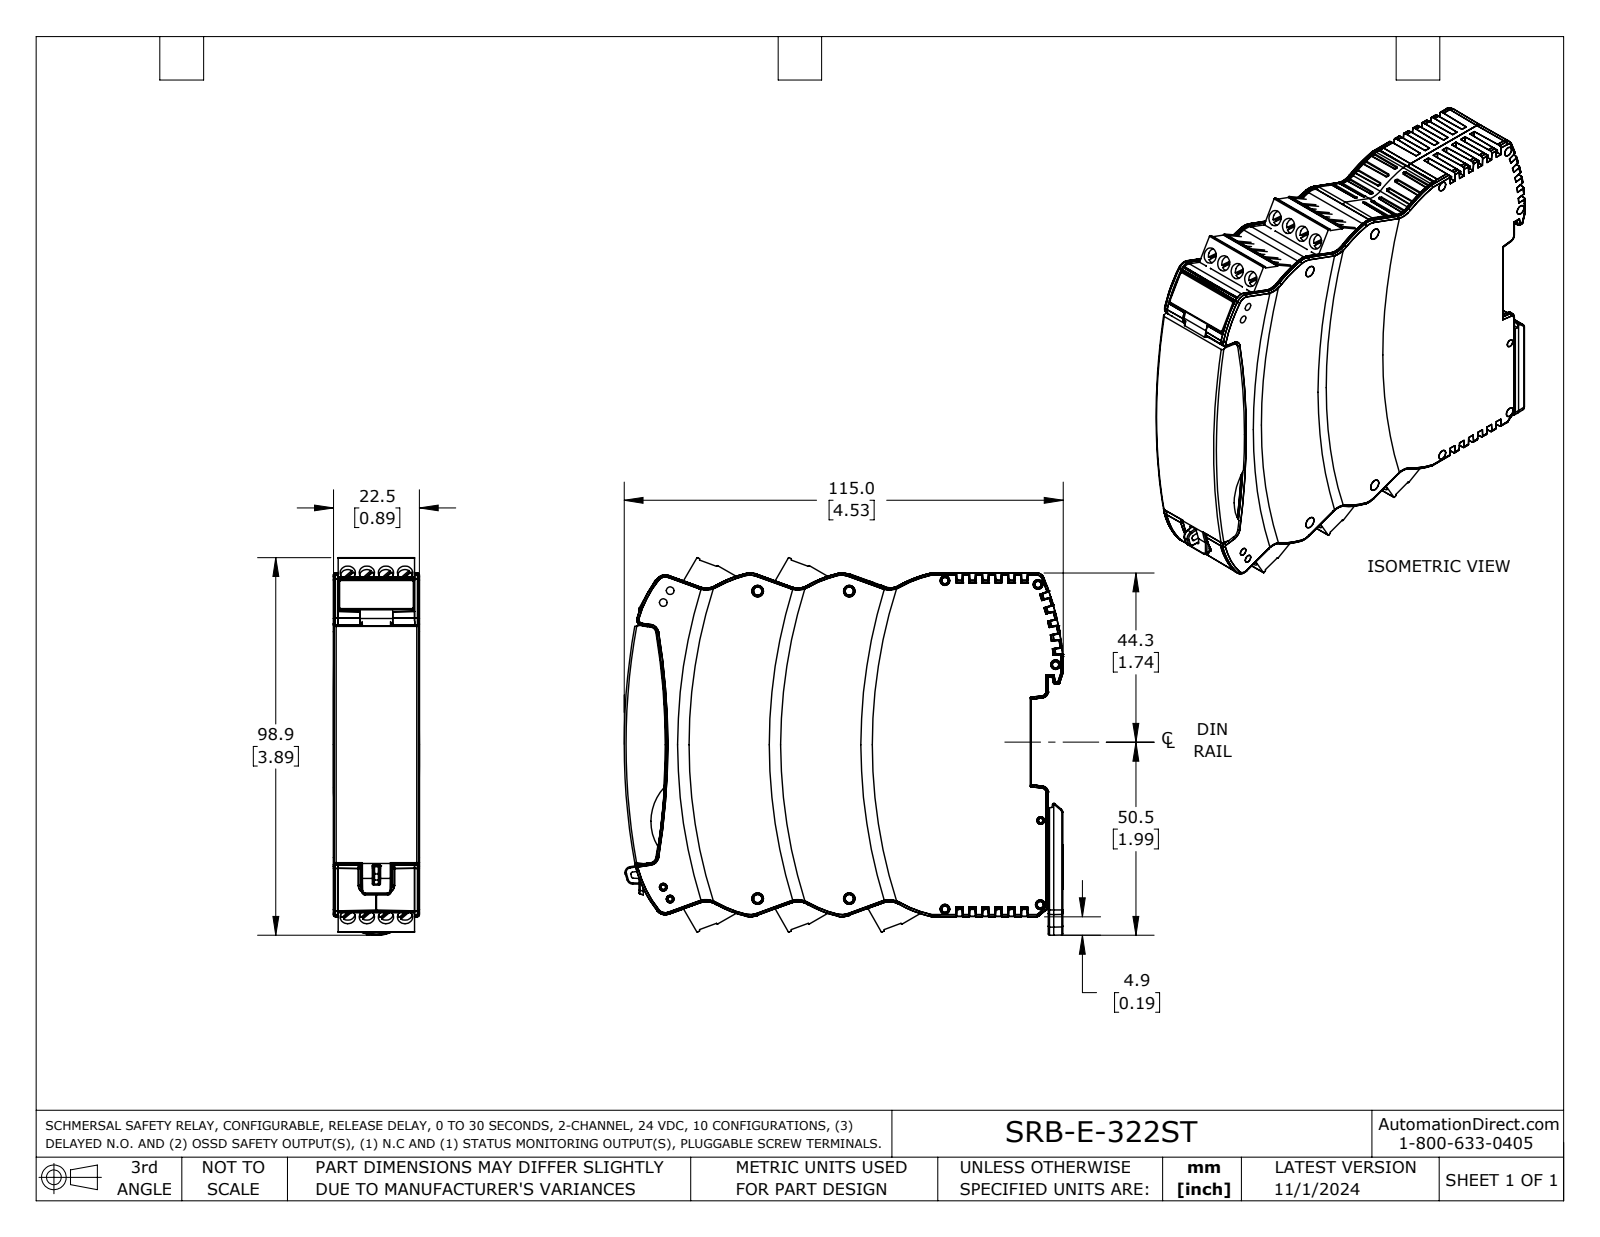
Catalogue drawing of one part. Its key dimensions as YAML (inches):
part_name: "SRB-E-322ST"
step_written_by: "SolidWorks 2023 (AUTOMOTIVE_DESIGN)"
units: inches
bodies: {solids: 2, faces: 3099, planar: 1661, cylindrical: 724, other: 714}
overall_size: [4.528, 3.893, 0.886]
volume: 12.97
surface_area: 64.5
round_holes:
  - {diameter: 0.157, count: 20}
round_bosses_or_shafts:
  - {diameter: 0.149, count: 20}
  - {diameter: 0.067, count: 1}
partial_cylinders:
  - {radius: 0.012, count: 174}
  - {radius: 0.02, count: 121}
  - {radius: 0.01, count: 60}
  - {radius: 0.008, count: 45}
  - {radius: 0.059, count: 26}
  - {radius: 0.039, count: 16}
  - {radius: 0.007, count: 10}
  - {radius: 0.079, count: 8}
face_to_face_distances: [0.886, 0.049, 0.837, 0.133, 0.267, 0.035, 0.134, 0.014, 0.85, 0.801]
hole_center_spacings: [0.197, 0.512, 0.394, 0.472, 0.615, 0.518, 0.972, 0.591]
